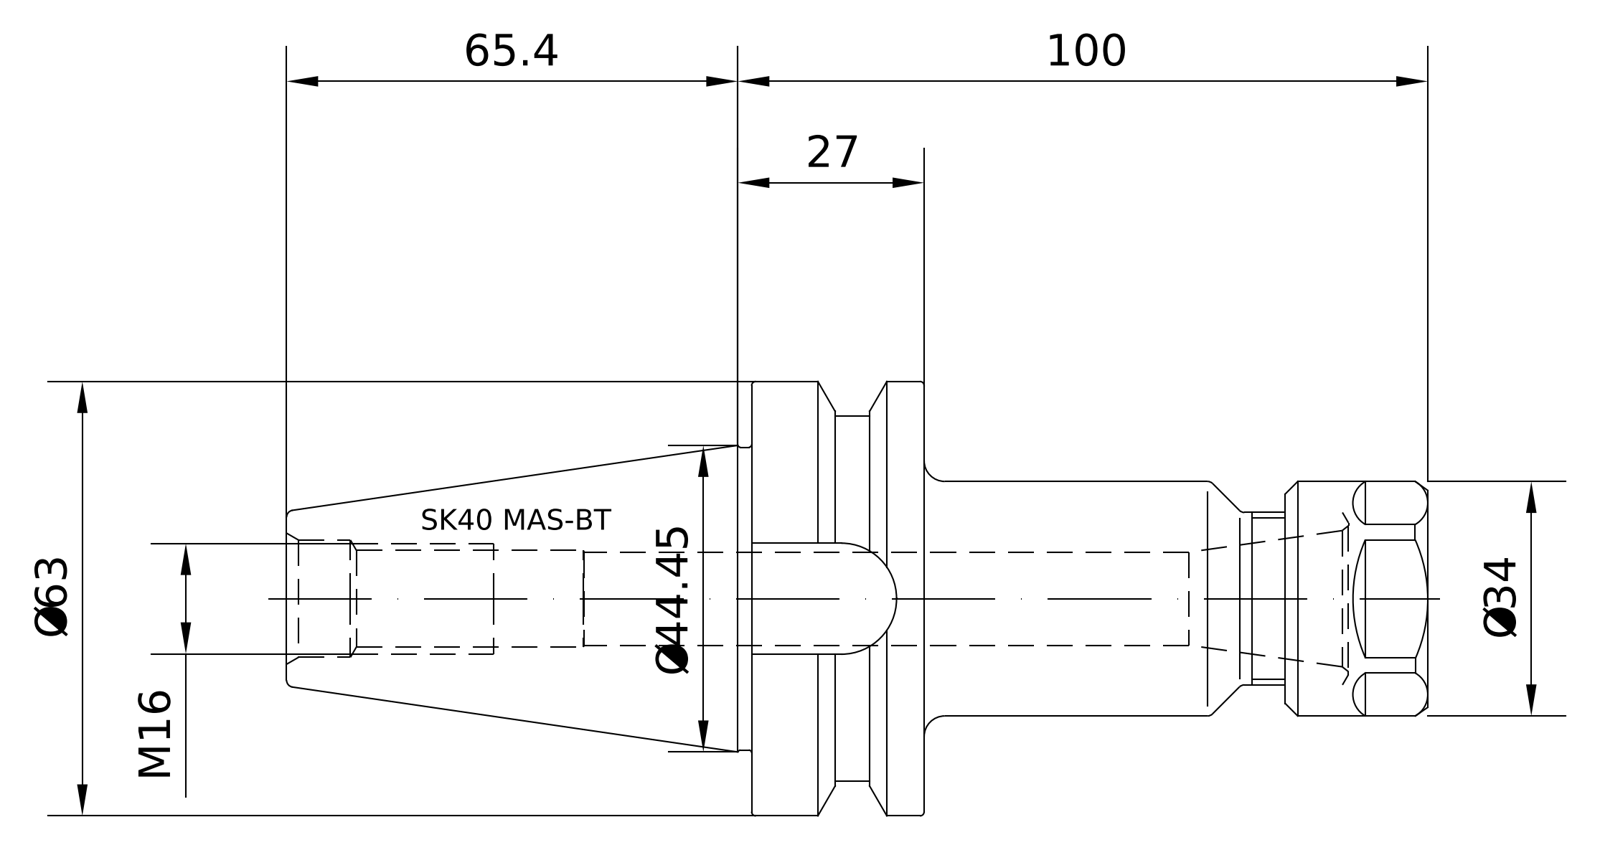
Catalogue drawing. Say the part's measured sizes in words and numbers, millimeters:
The part is named "40-521-20; 83-912-20; 40-521-20_ASM". Its 3-D file was written by "PRO/ENGINEER BY PARAMETRIC TECHNOLOGY CORPORATION, 2010430 (CONFIG_CONTROL_DESIGN)". It is 2 solids with 128 faces: 34 planar, 26 cylindrical and 68 other. Overall it measures 165.4 by 62.98 by 62.98 millimeters. Its volume is 184 533 cubic millimeters and its surface area 32 361 square millimeters. Round holes: 1 of diameter 13.5, 1 of diameter 13.84, 1 of diameter 17.01, 1 of diameter 17.5. Round bosses or shafts: 1 of diameter 62.98, 1 of diameter 52.75, 1 of diameter 43.75, 1 of diameter 34, 1 of diameter 25, 1 of diameter 16.01. Partial cylindrical surfaces (rounded edges, fillets, slot ends): 1 of radius 8.1. The main face-to-face distances are 25, 79, 54, 30, 98, 73, 19, 7.45, 37.45, 44.9.
